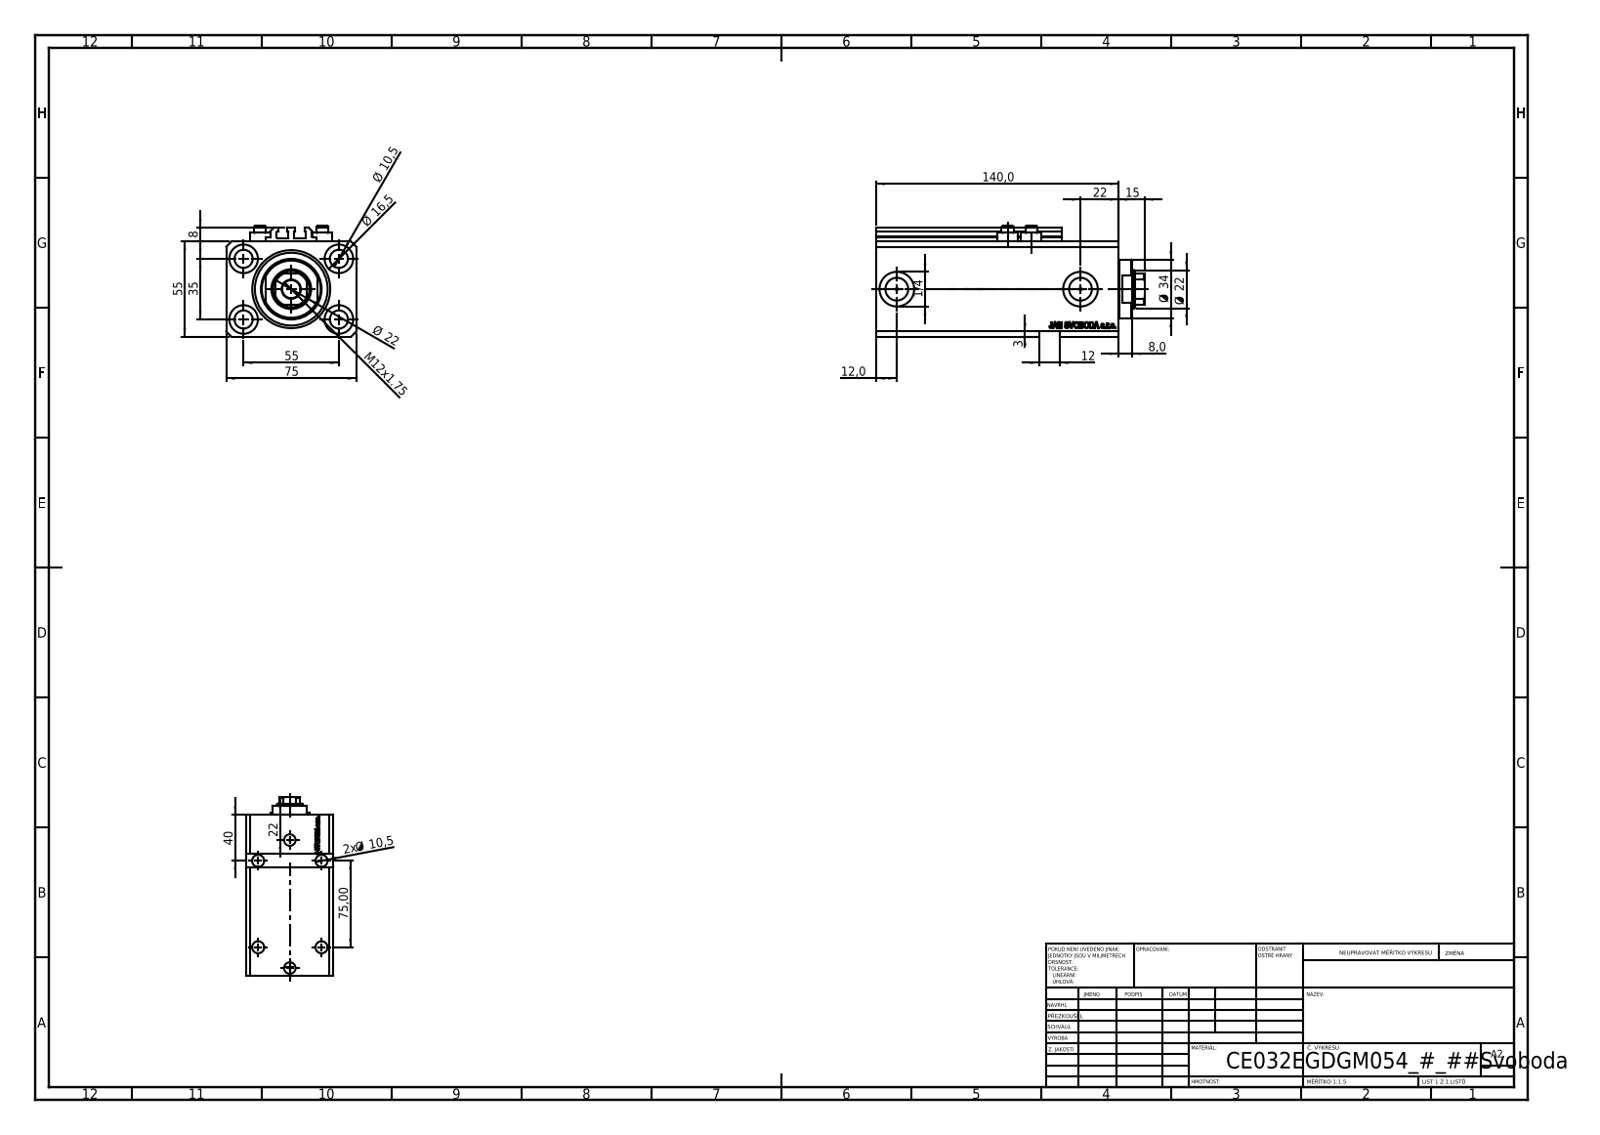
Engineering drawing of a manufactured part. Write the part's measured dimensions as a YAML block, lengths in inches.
part_name: "V250CE_VC_E; V250CE_E_Body; V250CE_C_VCP; ALLEN BOLT V250CE"
step_written_by: "SolidWorks 2019 (CONFIG_CONTROL_DESIGN)"
units: inches
bodies: {solids: 8, faces: 1100, planar: 518, cylindrical: 158, other: 424}
overall_size: [6.102, 2.953, 2.52]
volume: 29.39
surface_area: 180.5
round_holes:
  - {diameter: 0.413, count: 9}
  - {diameter: 0.049, count: 4}
  - {diameter: 0.157, count: 4}
  - {diameter: 0.65, count: 4}
  - {diameter: 0.394, count: 2}
  - {diameter: 0.518, count: 2}
  - {diameter: 0.787, count: 2}
  - {diameter: 0.866, count: 1}
  - {diameter: 1.26, count: 1}
  - {diameter: 1.772, count: 1}
round_bosses_or_shafts:
  - {diameter: 0.457, count: 4}
  - {diameter: 0.276, count: 4}
  - {diameter: 1.339, count: 1}
partial_cylinders:
  - {radius: 0.008, count: 10}
  - {radius: 0.413, count: 1}
face_to_face_distances: [2.165, 2.953, 0.591, 0.39, 5.512, 4.921, 0.118, 2.244, 4.531, 5.122]
hole_center_spacings: [1.283, 1.294, 2.165, 3.818, 0.535, 0.555, 1.016, 1.283]
